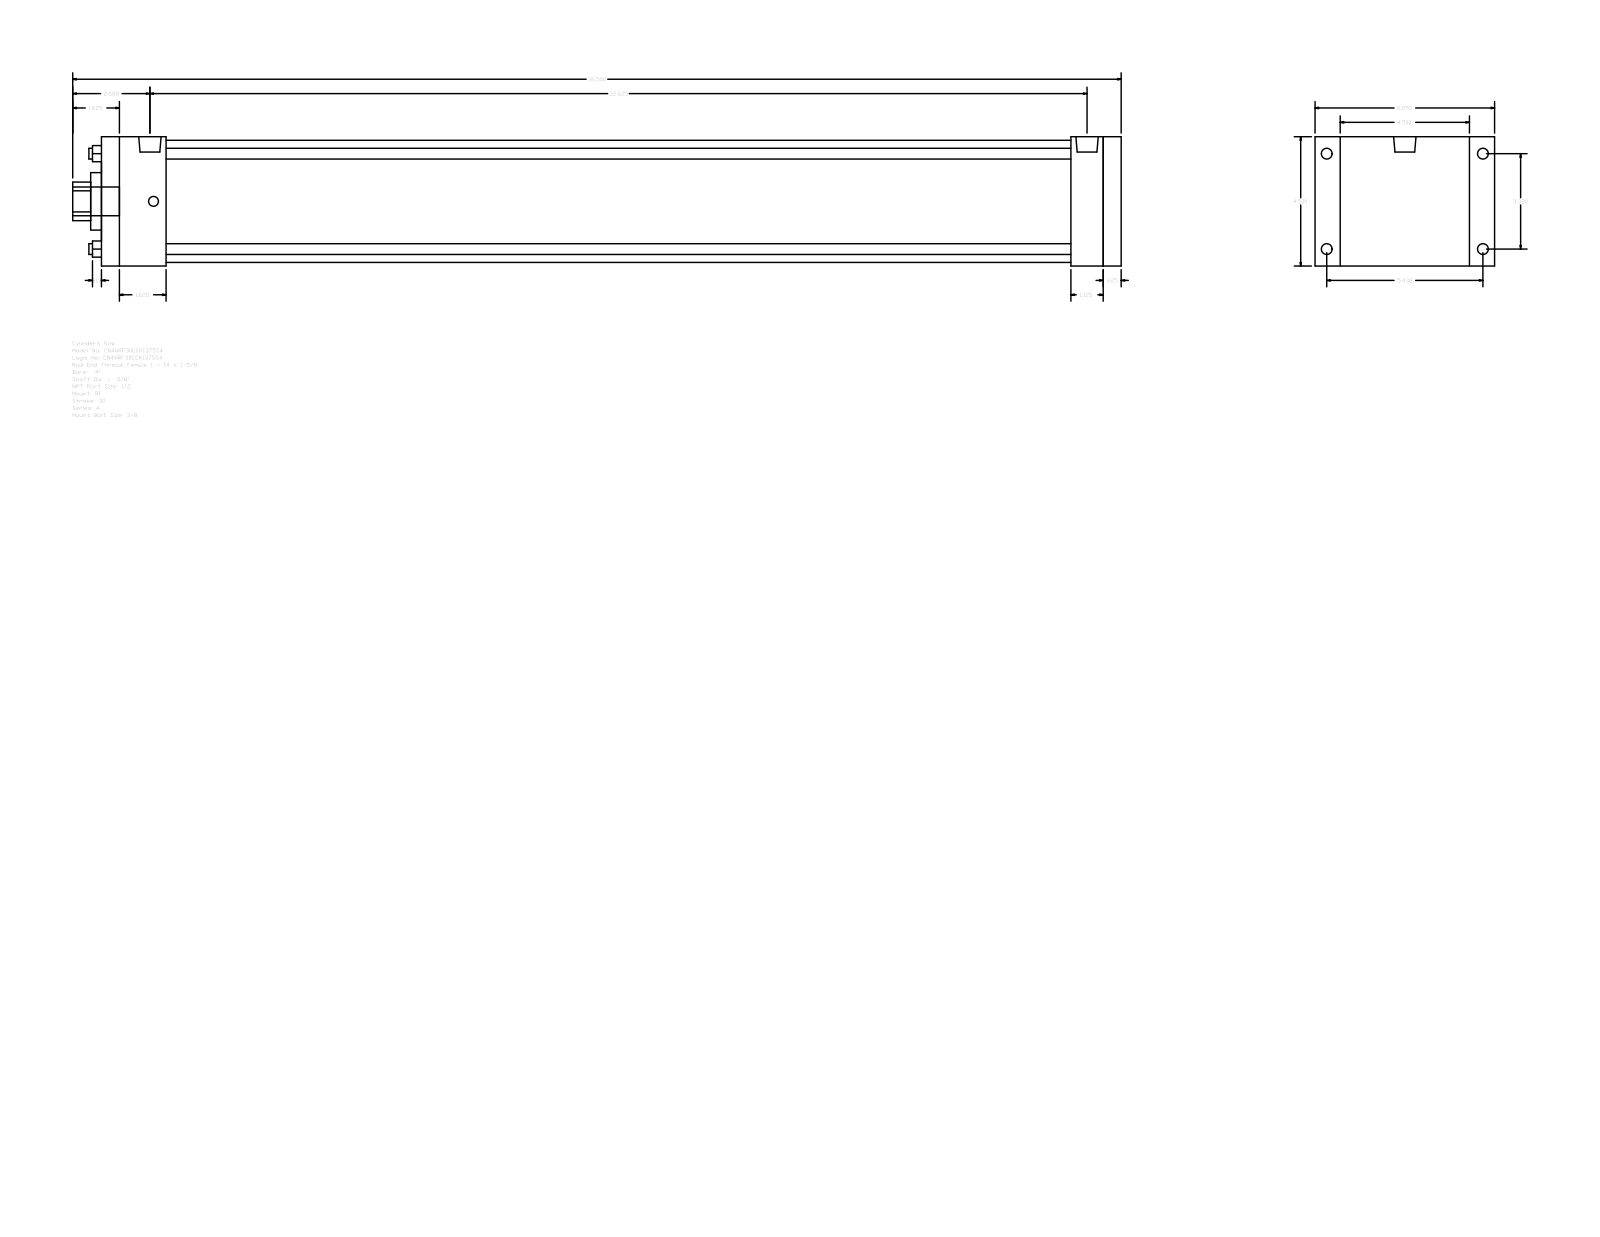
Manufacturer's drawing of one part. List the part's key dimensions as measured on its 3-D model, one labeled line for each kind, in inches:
Part name (STEP PRODUCT): A_RF__0400_1.375
STEP written by: GSSL Pune (CONFIG_CONTROL_DESIGN)
Units: inches
Bodies: 0 solids, 92 faces (64 planar, 28 cylindrical, 0 other)
Overall size (bounding box): 36.5 × 6.25 × 4.5
Round holes (diameter × count): ⌀0.375 ×4, ⌀1.375 ×1, ⌀2 ×1, ⌀4.25 ×1
Round bosses / shafts (diameter × count): ⌀0.375 ×4, ⌀0.344 ×4, ⌀0.778 ×2, ⌀1 ×1
Partial cylindrical surfaces — rounded edges, fillets, slot ends (radius × count): R0.672 ×1
Main face-to-face distances: 4.5, 35.5, 0.625, 34.875, 1.125, 0.875, 5.375, 33.75, 1.75, 2.25
Hole centre spacings: 2.347, 3.32, 4.695
